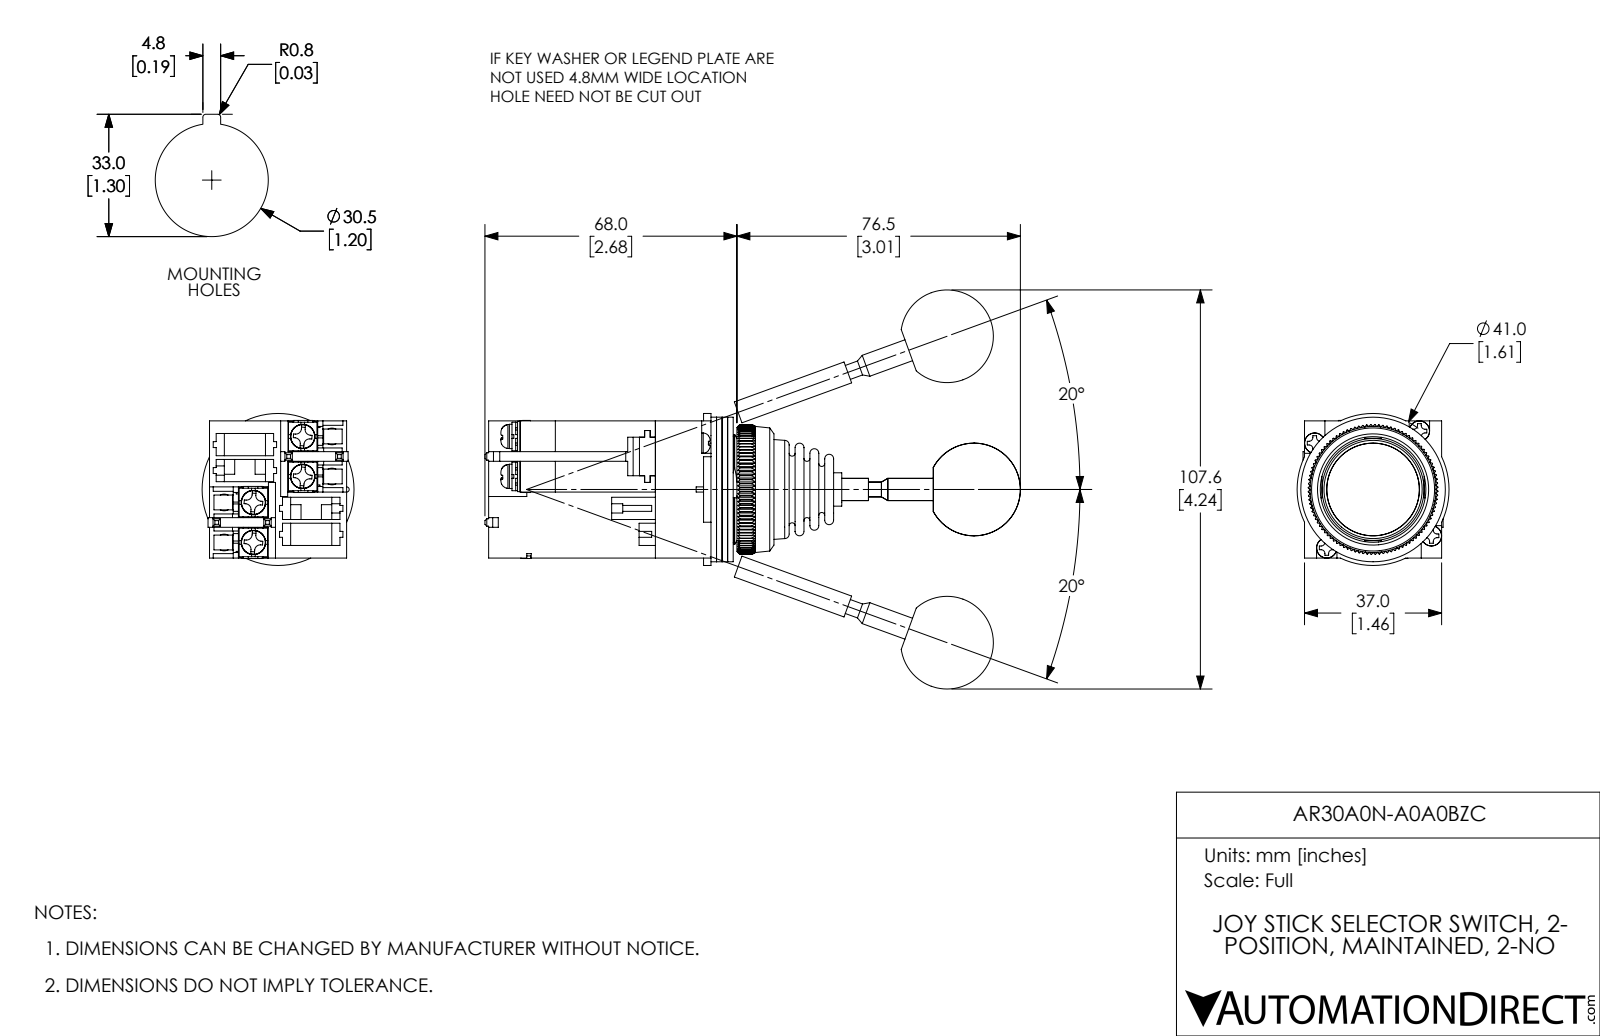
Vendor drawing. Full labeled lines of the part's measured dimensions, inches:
Part name (STEP PRODUCT): AR30A0N-A0A0BZC
STEP written by: SolidWorks 2017 (AUTOMOTIVE_DESIGN)
Units: inches
Bodies: 32 solids, 1971 faces (1388 planar, 321 cylindrical, 262 other)
Overall size (bounding box): 5.689 × 1.614 × 1.614
Volume: 4.184 in³ · Surface area: 68.68 in²
Round holes (diameter × count): ⌀0.118 ×8, ⌀0.138 ×4, ⌀0.142 ×4, ⌀0.315 ×1, ⌀0.874 ×1, ⌀1.122 ×1, ⌀1.173 ×1
Round bosses / shafts (diameter × count): ⌀0.26 ×4, ⌀1.535 ×1, ⌀1.181 ×1, ⌀0.984 ×1, ⌀0.354 ×1, ⌀0.236 ×1, ⌀0.157 ×1
Partial cylindrical surfaces — rounded edges, fillets, slot ends (radius × count): R0.039 ×16, R0.059 ×16, R0.029 ×8, R0.057 ×8, R0.089 ×8, R0.108 ×4, R0.028 ×1, R0.398 ×1
Main face-to-face distances: 0.059, 0.701, 0.756, 0.055, 0.118, 1.457, 0.177, 0.236, 0.449, 0.114
Hole centre spacings: 0.792, 1.12, 0.296, 0.365, 0.424, 0.756, 0.875, 1.583
